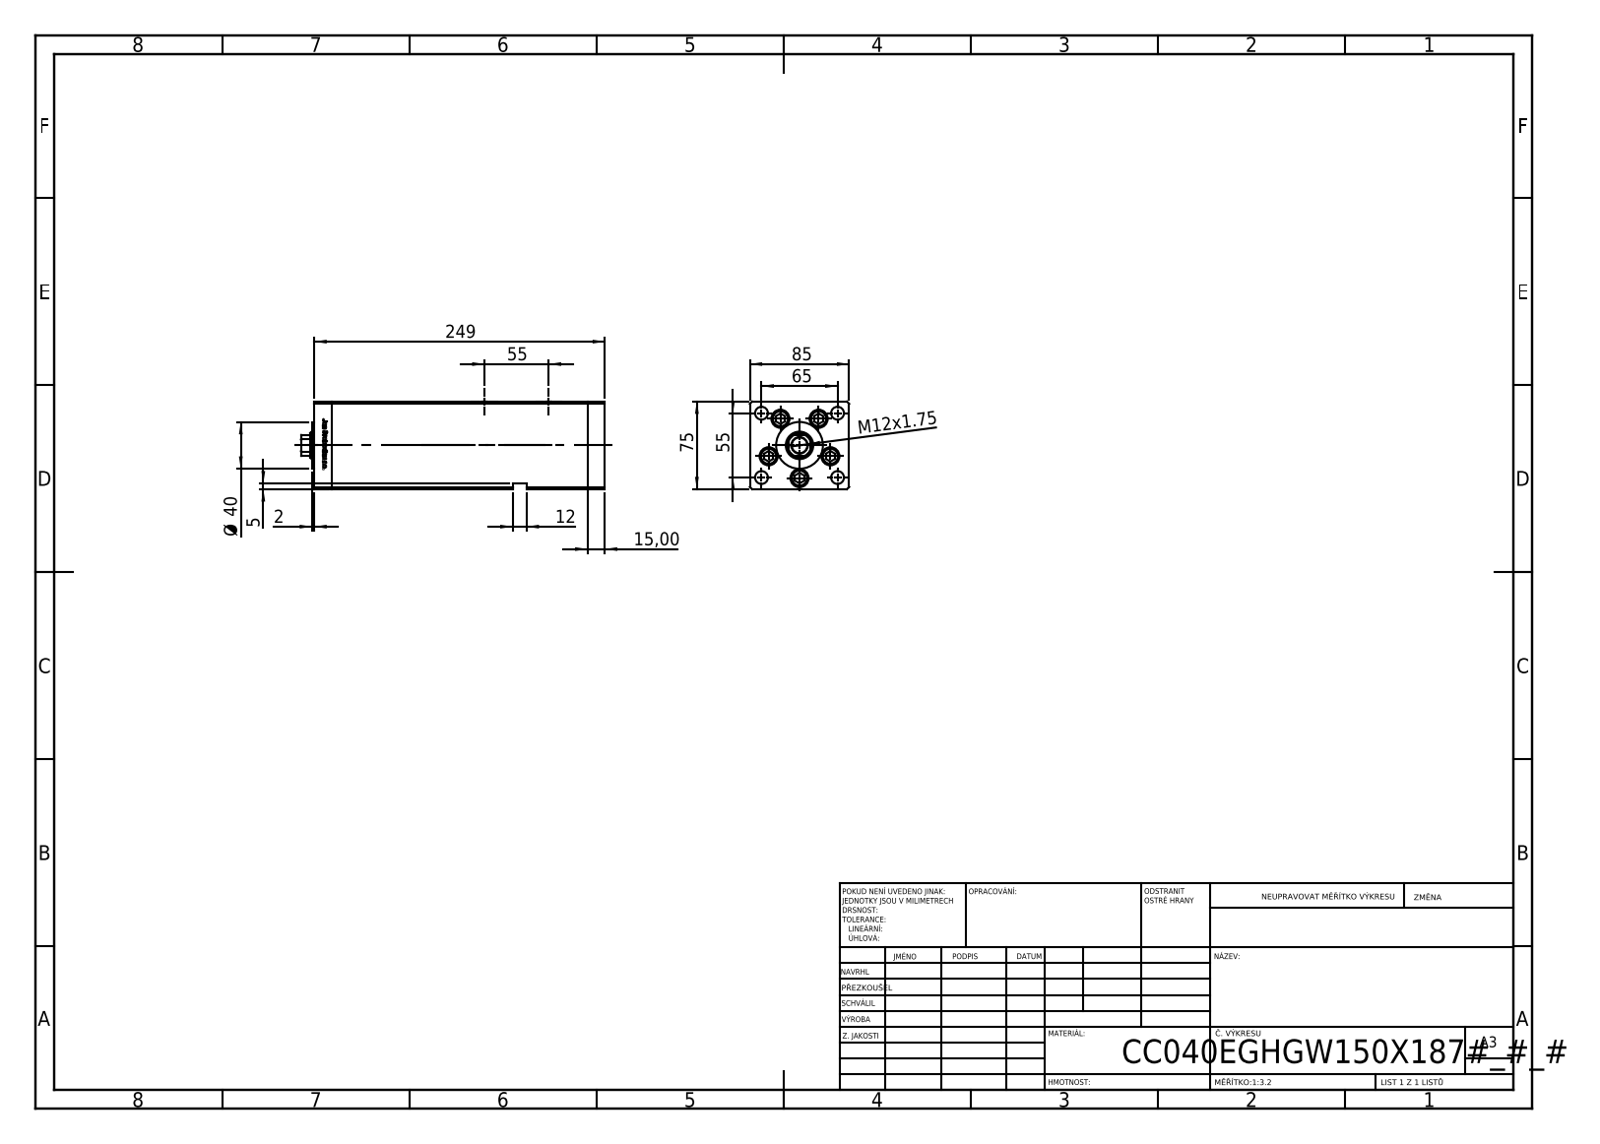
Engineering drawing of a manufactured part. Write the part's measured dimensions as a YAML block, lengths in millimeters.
part_name: "V220C_FRONT_E; V220C BACK_E; ALLEN BOLT; V220C_VC_E (+1 more)"
step_written_by: "SolidWorks 2019 (CONFIG_CONTROL_DESIGN)"
units: millimeters
bodies: {solids: 14, faces: 1212, planar: 473, cylindrical: 165, other: 574}
overall_size: [260, 85, 75]
volume: 1341000
surface_area: 209531
round_holes:
  - {diameter: 11, count: 9}
  - {diameter: 15.5, count: 5}
  - {diameter: 10.5, count: 4}
  - {diameter: 16.5, count: 4}
  - {diameter: 2, count: 2}
  - {diameter: 13.16, count: 2}
  - {diameter: 13.5, count: 1}
  - {diameter: 22, count: 1}
  - {diameter: 23.5, count: 1}
round_bosses_or_shafts:
  - {diameter: 14.5, count: 5}
  - {diameter: 8, count: 5}
  - {diameter: 40, count: 1}
partial_cylinders:
  - {radius: 0.93, count: 2}
  - {radius: 10.5, count: 1}
face_to_face_distances: [85, 75, 15, 218.5, 233.5, 10.5, 248.5, 68.5, 34.25, 64.5]
hole_center_spacings: [28, 42.57, 55, 65, 85.15, 16.86, 19.17, 32.33]
